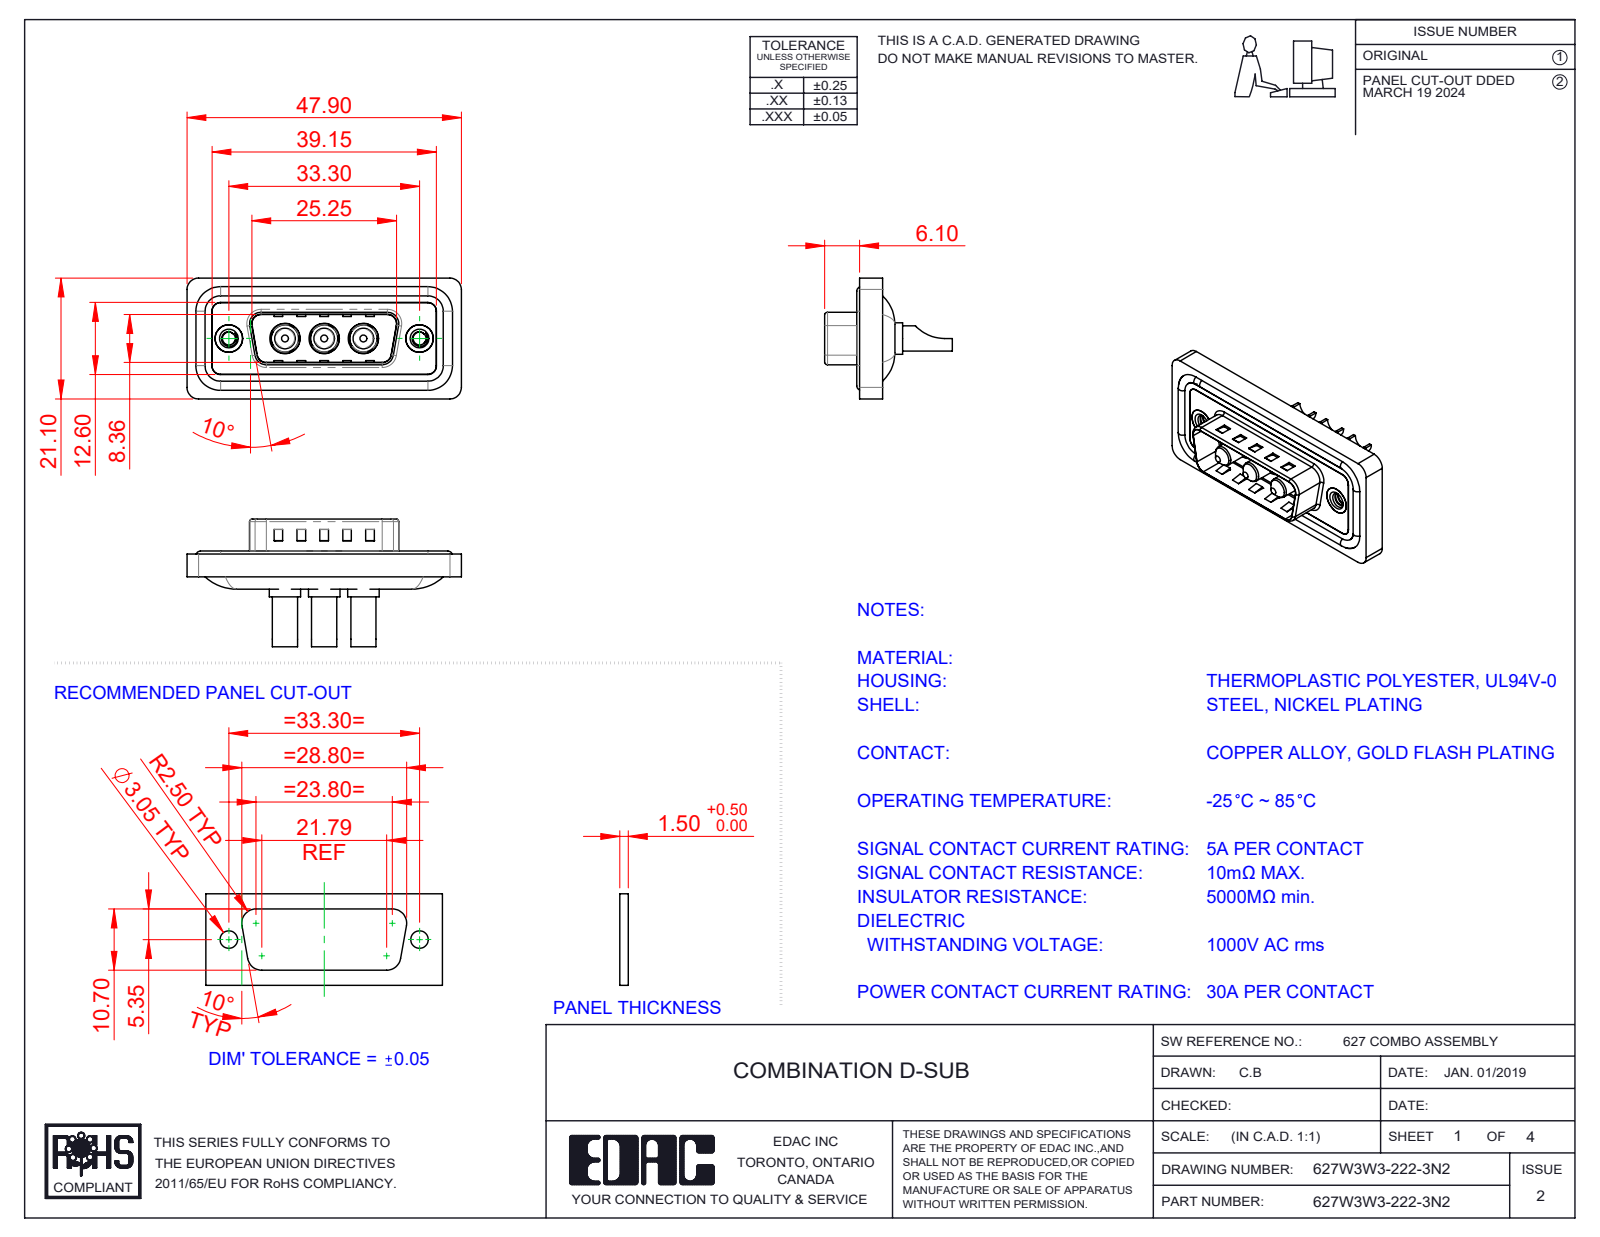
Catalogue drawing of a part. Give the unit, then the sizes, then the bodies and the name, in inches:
Units: inches
Overall size (bounding box): 1.886 × 0.878 × 0.831
Round holes (diameter × count): ⌀0.138 ×3, ⌀0.191 ×3, ⌀0.209 ×3, ⌀0.089 ×2, ⌀0.157 ×2, ⌀0.189 ×2, ⌀0.197 ×2
Round bosses / shafts (diameter × count): ⌀0.063 ×4, ⌀0.217 ×3, ⌀0.205 ×3, ⌀0.187 ×3, ⌀0.173 ×3, ⌀0.148 ×3, ⌀0.142 ×3, ⌀0.193 ×2
Partial cylindrical surfaces — rounded edges, fillets, slot ends (radius × count): R0.059 ×26, R0.079 ×20, R0.02 ×8, R0.063 ×8, R0.01 ×4, R0.024 ×4, R0.026 ×4, R0.035 ×4
Main face-to-face distances: 0.016, 0.043, 0.02, 0.063, 0.059, 0.122, 0.114, 0.032, 0.377, 0.098
Hole centre spacings: 0.27, 0.386, 0.656, 0.925, 0.539, 1.311
Volume: 0.345 in³ · Surface area: 14.07 in²
Bodies: 13 solids, 582 faces (216 planar, 250 cylindrical, 116 other)
Part name (STEP PRODUCT): 627Combo Shell Rear_15 Contacts; 627Combo Threaded Rivet_2; 627Combo Waterproof Housing_15 Contacts; 627Combo Housing_3W3 (+3 more)
STEP written by: SolidWorks 2023 (CONFIG_CONTROL_DESIGN)
